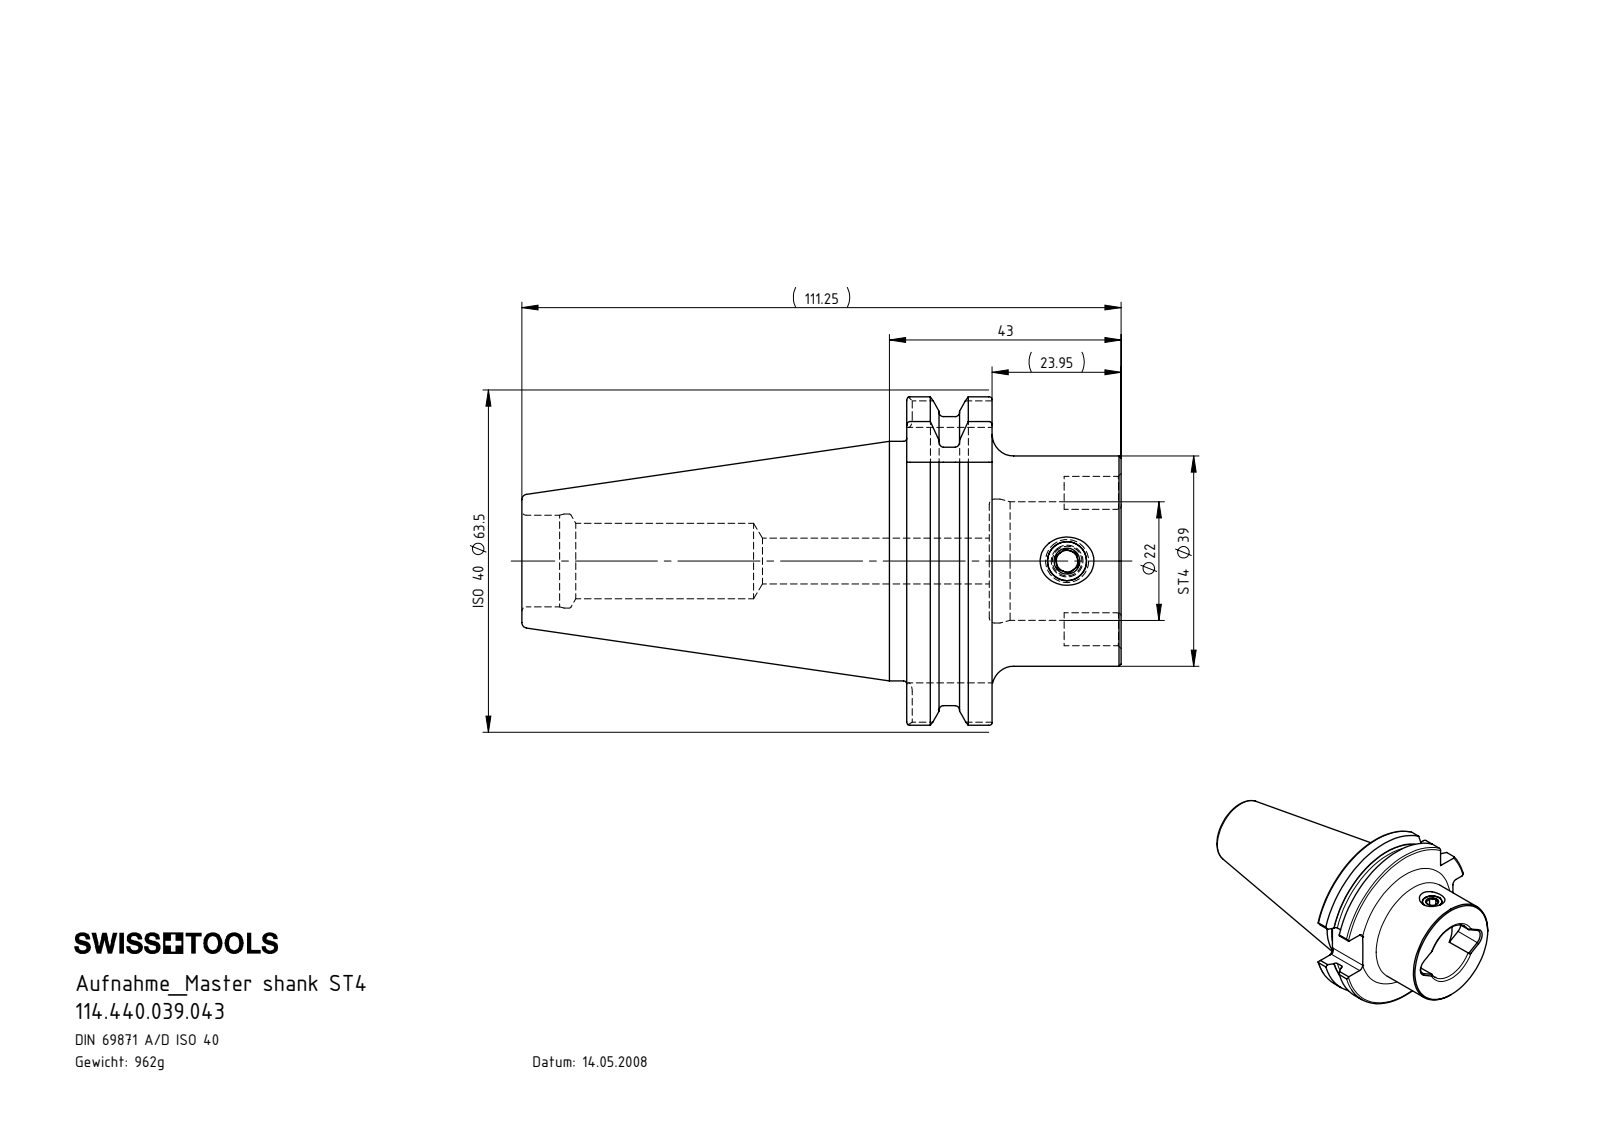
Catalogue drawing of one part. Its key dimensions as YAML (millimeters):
part_name: "ST4-ER1.001.011_A; SK4-ST4.K01.043_B; SK4.ST4.K01.043"
step_written_by: "SolidWorks 2017 (AUTOMOTIVE_DESIGN)"
units: millimeters
bodies: {solids: 2, faces: 126, planar: 54, cylindrical: 30, other: 42}
overall_size: [111.25, 63.5, 60.94]
volume: 122582
surface_area: 24509
round_holes:
  - {diameter: 4, count: 1}
  - {diameter: 7.25, count: 1}
  - {diameter: 8.5, count: 1}
  - {diameter: 14, count: 1}
  - {diameter: 17, count: 1}
  - {diameter: 17.45, count: 1}
  - {diameter: 22, count: 1}
  - {diameter: 23, count: 1}
round_bosses_or_shafts:
  - {diameter: 44.45, count: 1}
  - {diameter: 39, count: 1}
  - {diameter: 8, count: 1}
partial_cylinders:
  - {radius: 1.6, count: 8}
  - {radius: 3.2, count: 2}
  - {radius: 28, count: 1}
  - {radius: 31.75, count: 1}
face_to_face_distances: [15.85, 39.8, 23.95, 15.3, 0.55, 24.5, 47.4, 71.45, 86.75, 87.3]
